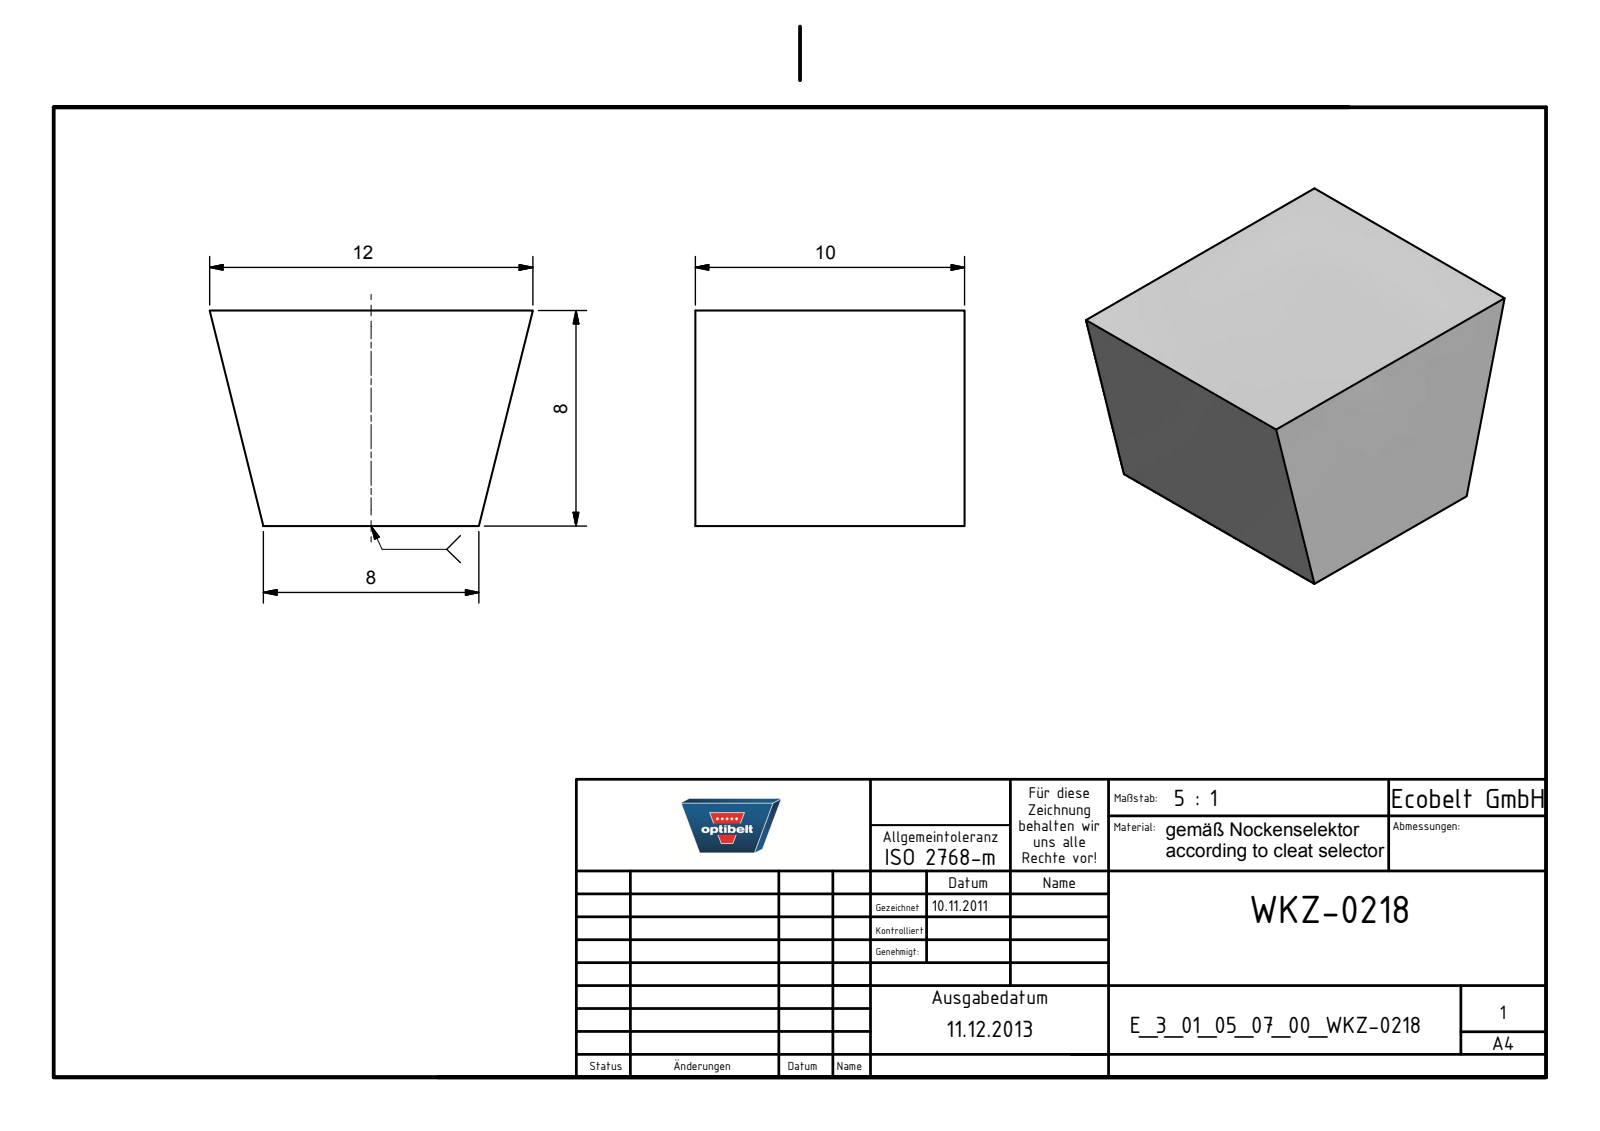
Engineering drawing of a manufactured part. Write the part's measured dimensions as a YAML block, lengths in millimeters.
part_name: "E_3_01_05_07_00_WKZ-0218"
step_written_by: "Autodesk Inventor 2025 (AUTOMOTIVE_DESIGN)"
units: millimeters
bodies: {solids: 1, faces: 6, planar: 6, cylindrical: 0, other: 0}
overall_size: [12, 10, 8]
volume: 800
surface_area: 525
face_to_face_distances: [8, 10]
